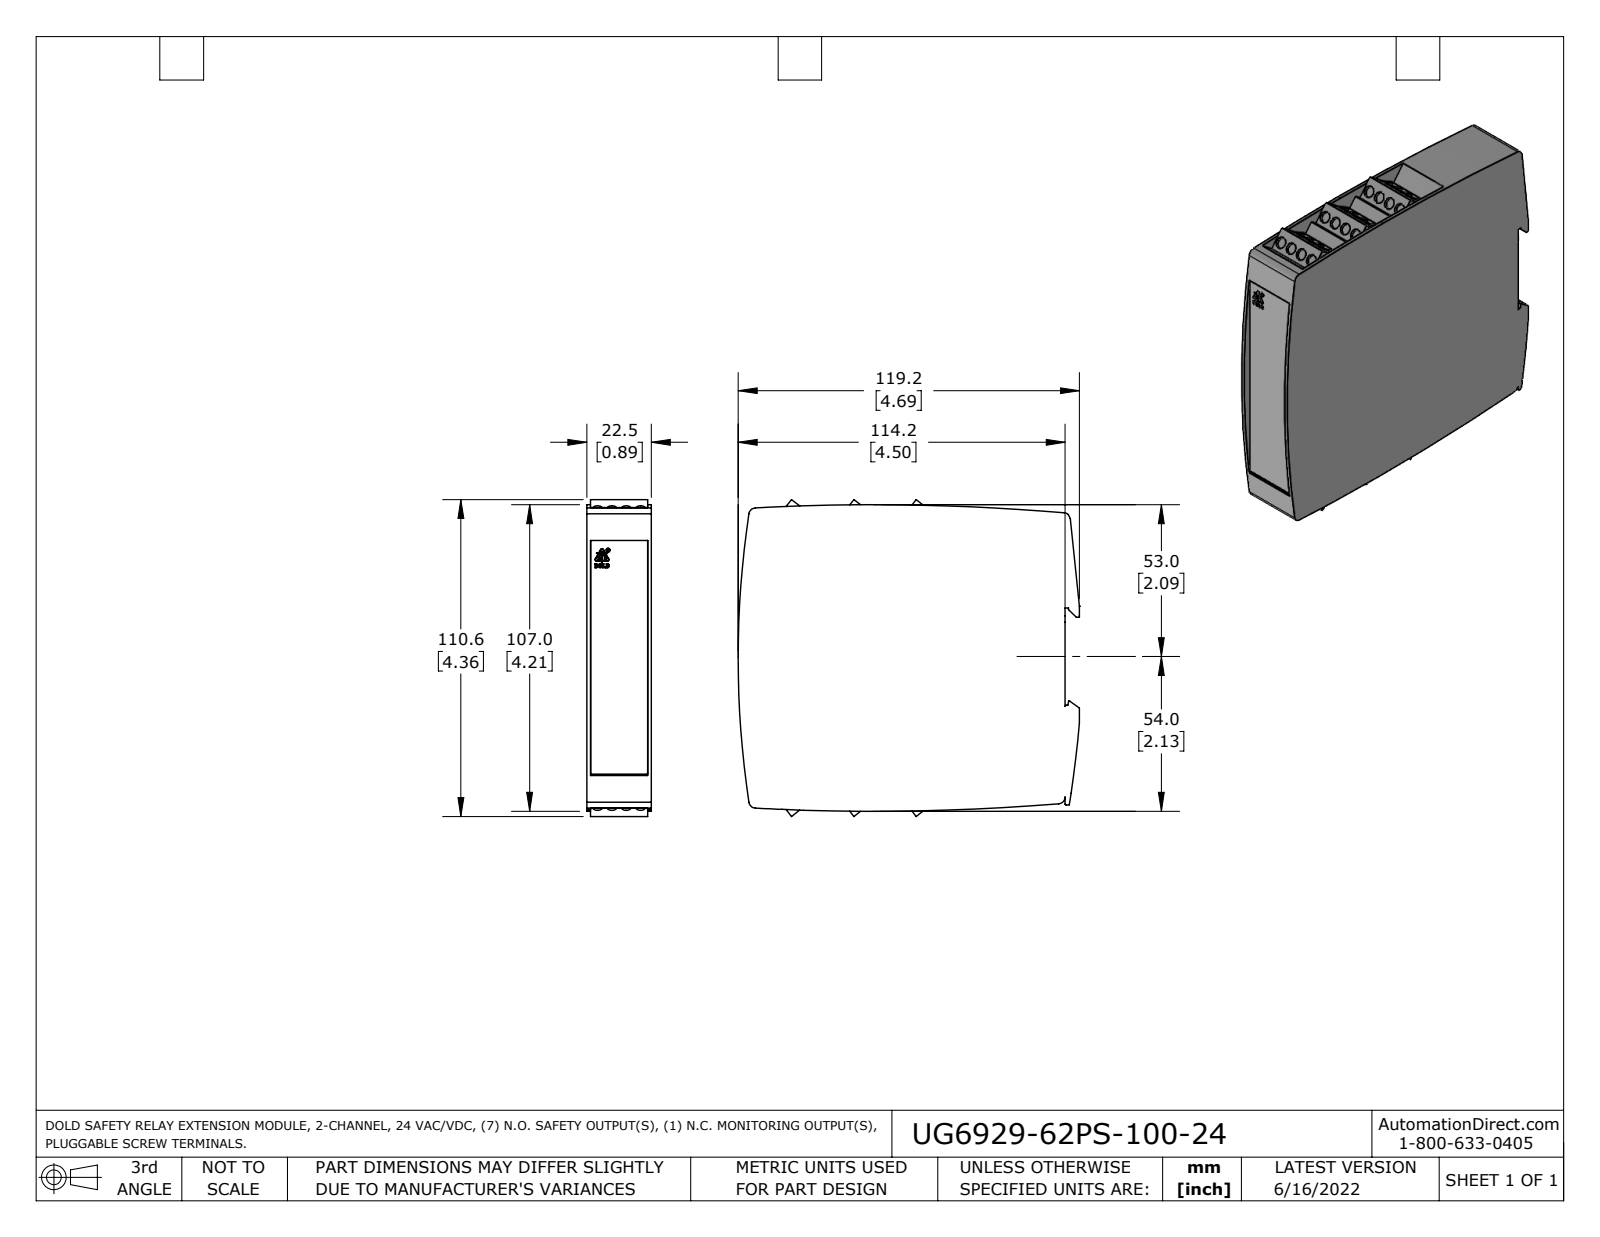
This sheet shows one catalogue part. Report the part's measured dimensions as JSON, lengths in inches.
{"part_name": "UG6929-62PS-100-24", "step_written_by": "SolidWorks 2021 (AUTOMOTIVE_DESIGN)", "units": "inches", "bodies": {"solids": 1, "faces": 666, "planar": 570, "cylindrical": 95, "other": 1}, "overall_size": [4.693, 4.355, 0.886], "volume_in3": 16, "surface_area_in2": 58.45, "round_holes": [[0.157, 24], [0.053, 1]], "round_bosses_or_shafts": [[0.049, 1]], "partial_cylinders_radius": [[0.004, 12], [0.012, 12], [0.094, 7], [0.005, 6], [0.004, 4], [31.496, 4], [0.021, 3], [0.012, 2]], "face_to_face_distances": [0.886, 0.049, 0.837, 0.528, 0.675, 4.379, 0.787, 1.35, 1.056, 0.566], "hole_center_spacings": [0.197, 0.394, 0.563, 0.563, 1.074, 0.528, 0.528, 0.658]}
